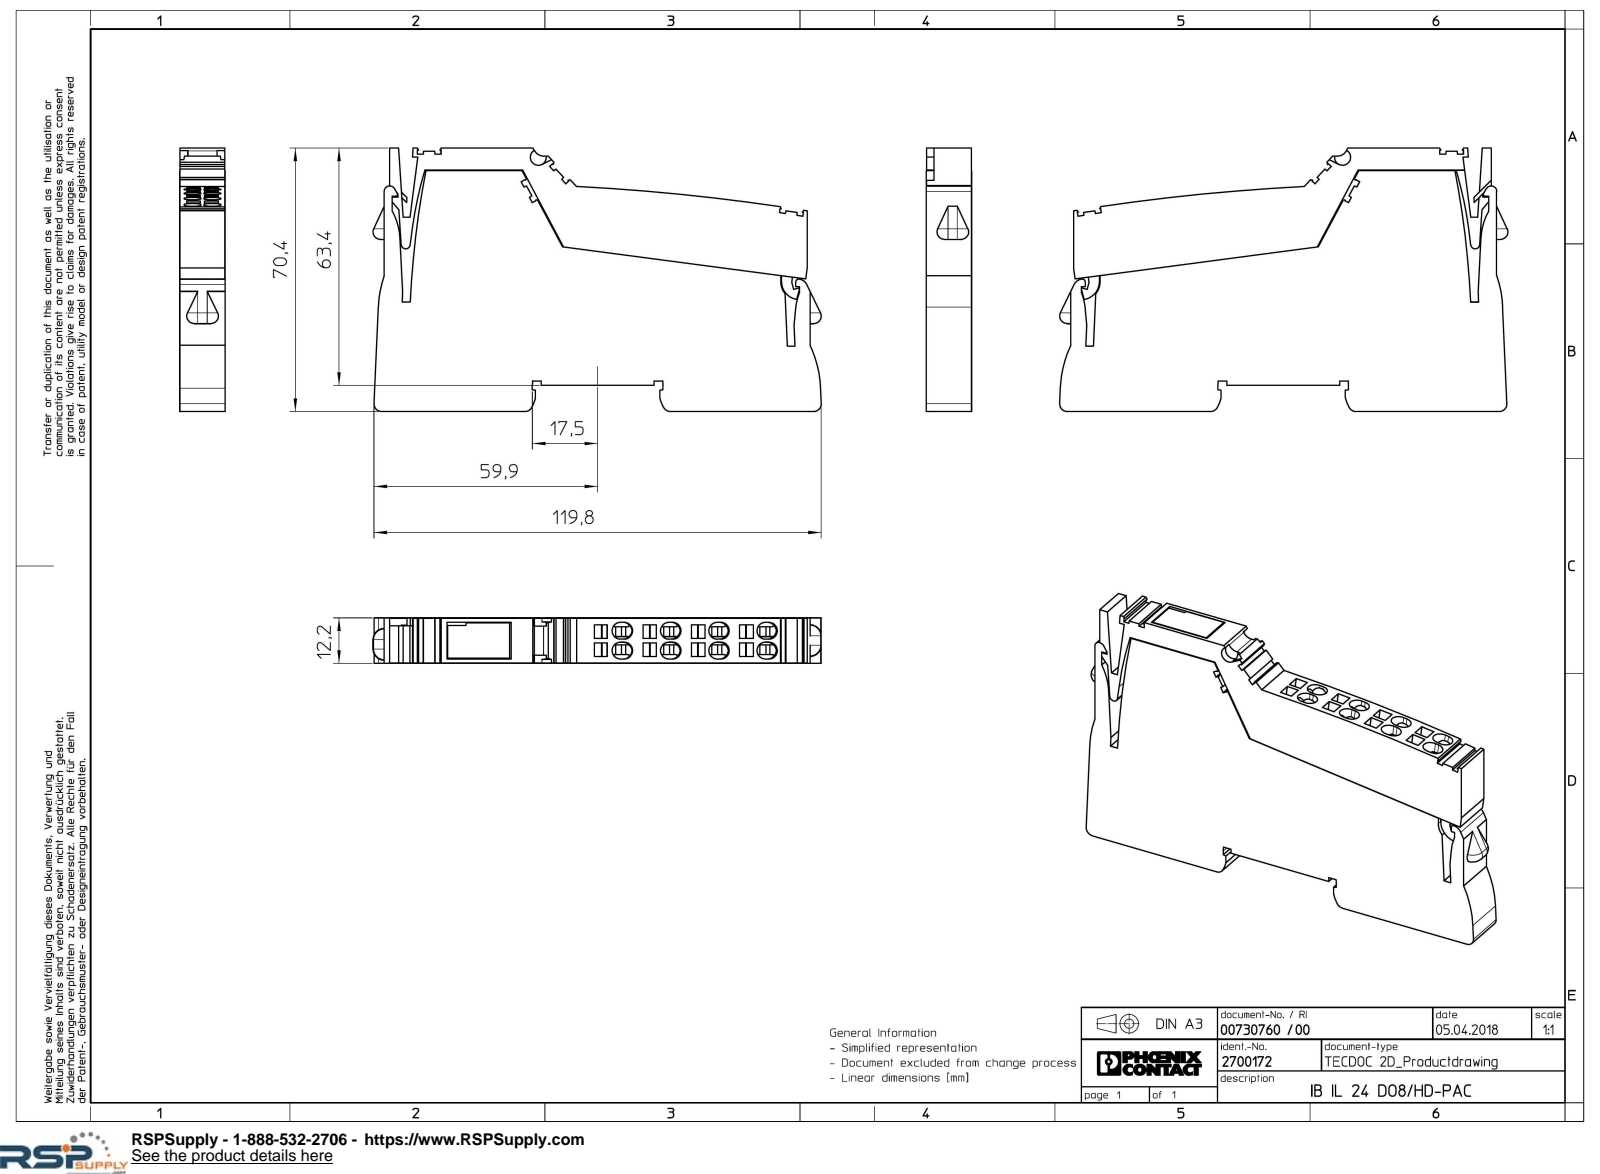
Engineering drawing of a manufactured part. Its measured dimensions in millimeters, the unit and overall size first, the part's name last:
Units: millimetres
Overall size (bounding box): 120.11 × 70.43 × 12.15
Round holes (diameter × count): ⌀1.2 ×6
Partial cylindrical surfaces — rounded edges, fillets, slot ends (radius × count): R2.25 ×16, R2 ×6, R0.15 ×2, R0.6 ×2, R8.5 ×2, R9.5 ×2, R16.7 ×2, R30 ×2
Main face-to-face distances: 12.15, 12.1, 12.05, 12, 25.99, 3.3, 4.8, 64.4, 12.99, 1.2
Hole centre spacings: 13, 13.86, 4.8, 26, 26.44
Volume: 80 108 mm³ · Surface area: 28 085 mm²
Bodies: 3 solids, 598 faces (501 planar, 61 cylindrical, 36 other)
Part name (STEP PRODUCT): L-L_ST_GN_6021-select; L_L_2_GEH_GN_6021-select; L_L_LWL_PK_AUSSEN-select; IB_IL_24_DO8_HD_PAC-select
STEP written by: Creo Elements/Direct Modeling 18.1I 14-Aug-2016 (C) Parametric Technology GmbH (AUTOMOTIVE_DESIGN)
